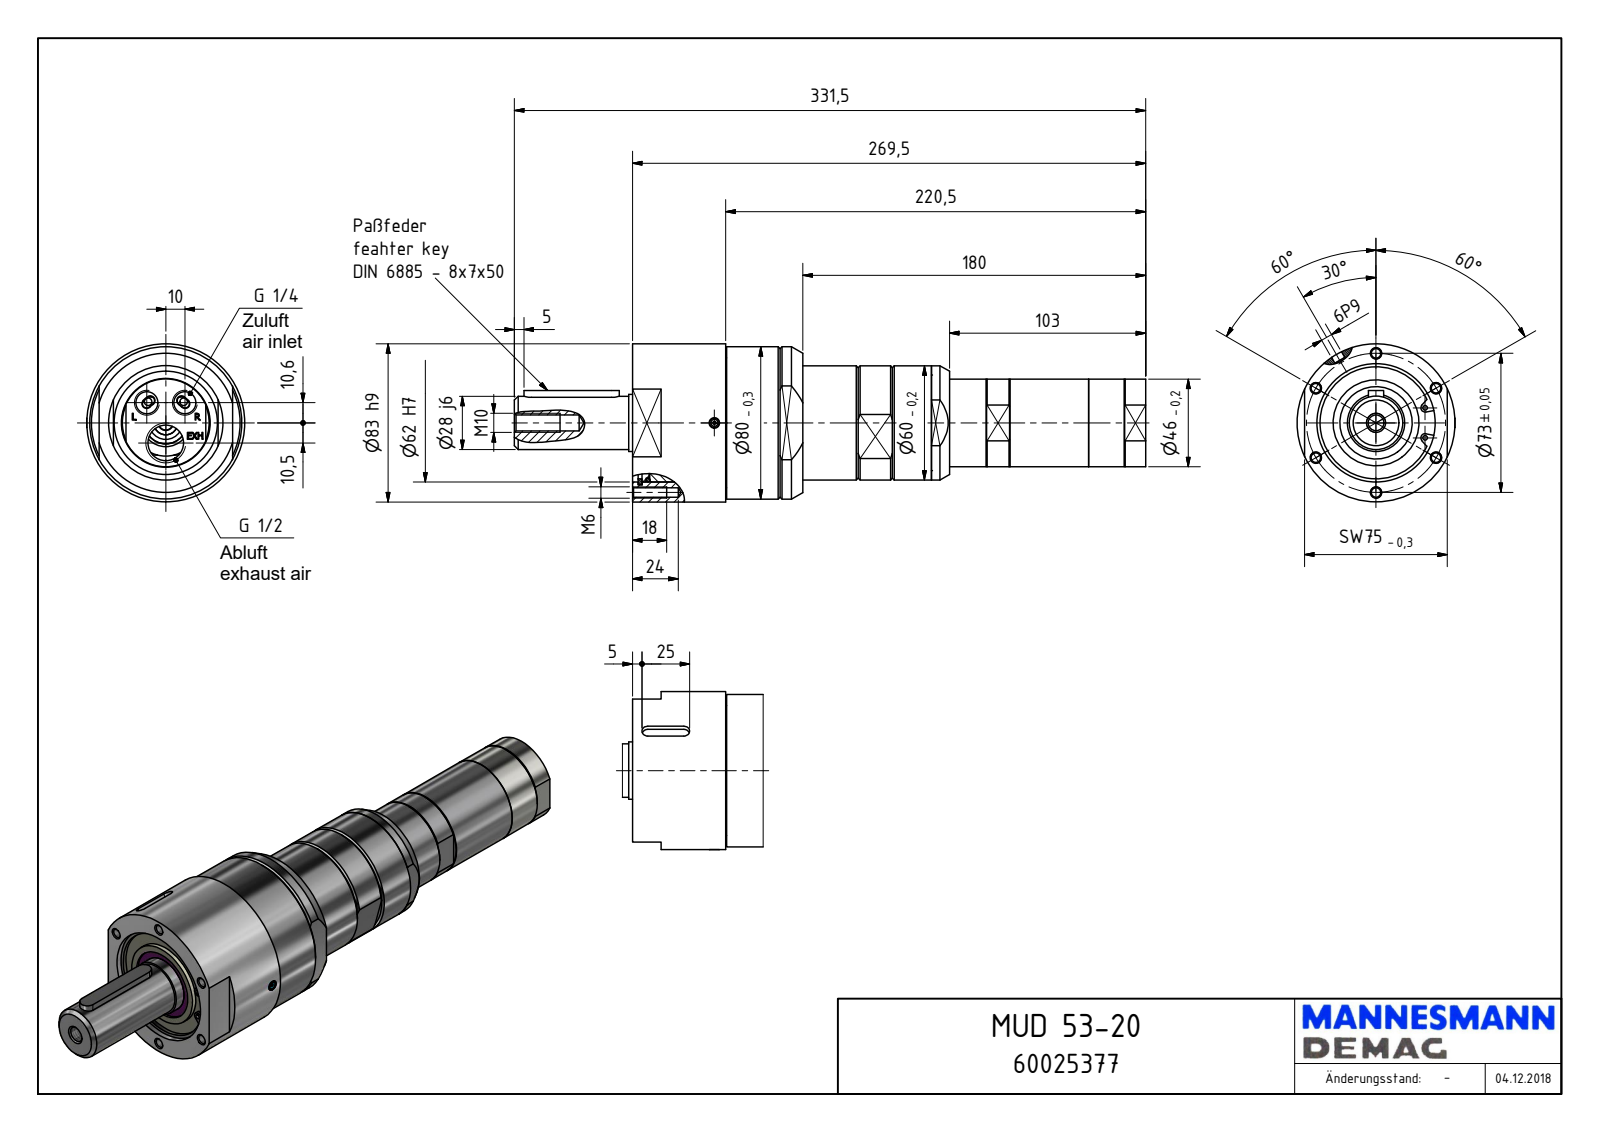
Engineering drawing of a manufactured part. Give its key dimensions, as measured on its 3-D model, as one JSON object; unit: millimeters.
{"part_name": "MUD 53-20_60025377", "step_written_by": "Autodesk Inventor 2018 (AUTOMOTIVE_DESIGN)", "units": "millimeters", "bodies": {"solids": 1, "faces": 573, "planar": 234, "cylindrical": 273, "other": 66}, "overall_size": [331.5, 83, 83], "volume_mm3": 862785, "surface_area_mm2": 88003, "round_holes": [[4.92, 6], [1.55, 3], [2.5, 2], [4, 2], [5.5, 2], [11.45, 2], [8.38, 1], [18.63, 1], [36.5, 1], [38, 1], [40, 1], [46.5, 1]], "round_bosses_or_shafts": [[5, 2], [3.6, 2], [83, 1], [80, 1], [68.18, 1], [60, 1], [54.45, 1], [46, 1]], "partial_cylinders_radius": [[3.5, 94], [2.25, 2], [3, 2], [4, 2], [5, 2], [24.62, 1], [24.96, 1], [32.5, 1]], "face_to_face_distances": [2.5, 0.5, 157, 49, 89.5, 40.5, 5, 44, 84.5, 49.5], "hole_center_spacings": [36.5, 63.22, 73, 11.89, 14.57, 22.92, 23.35, 26.77]}
